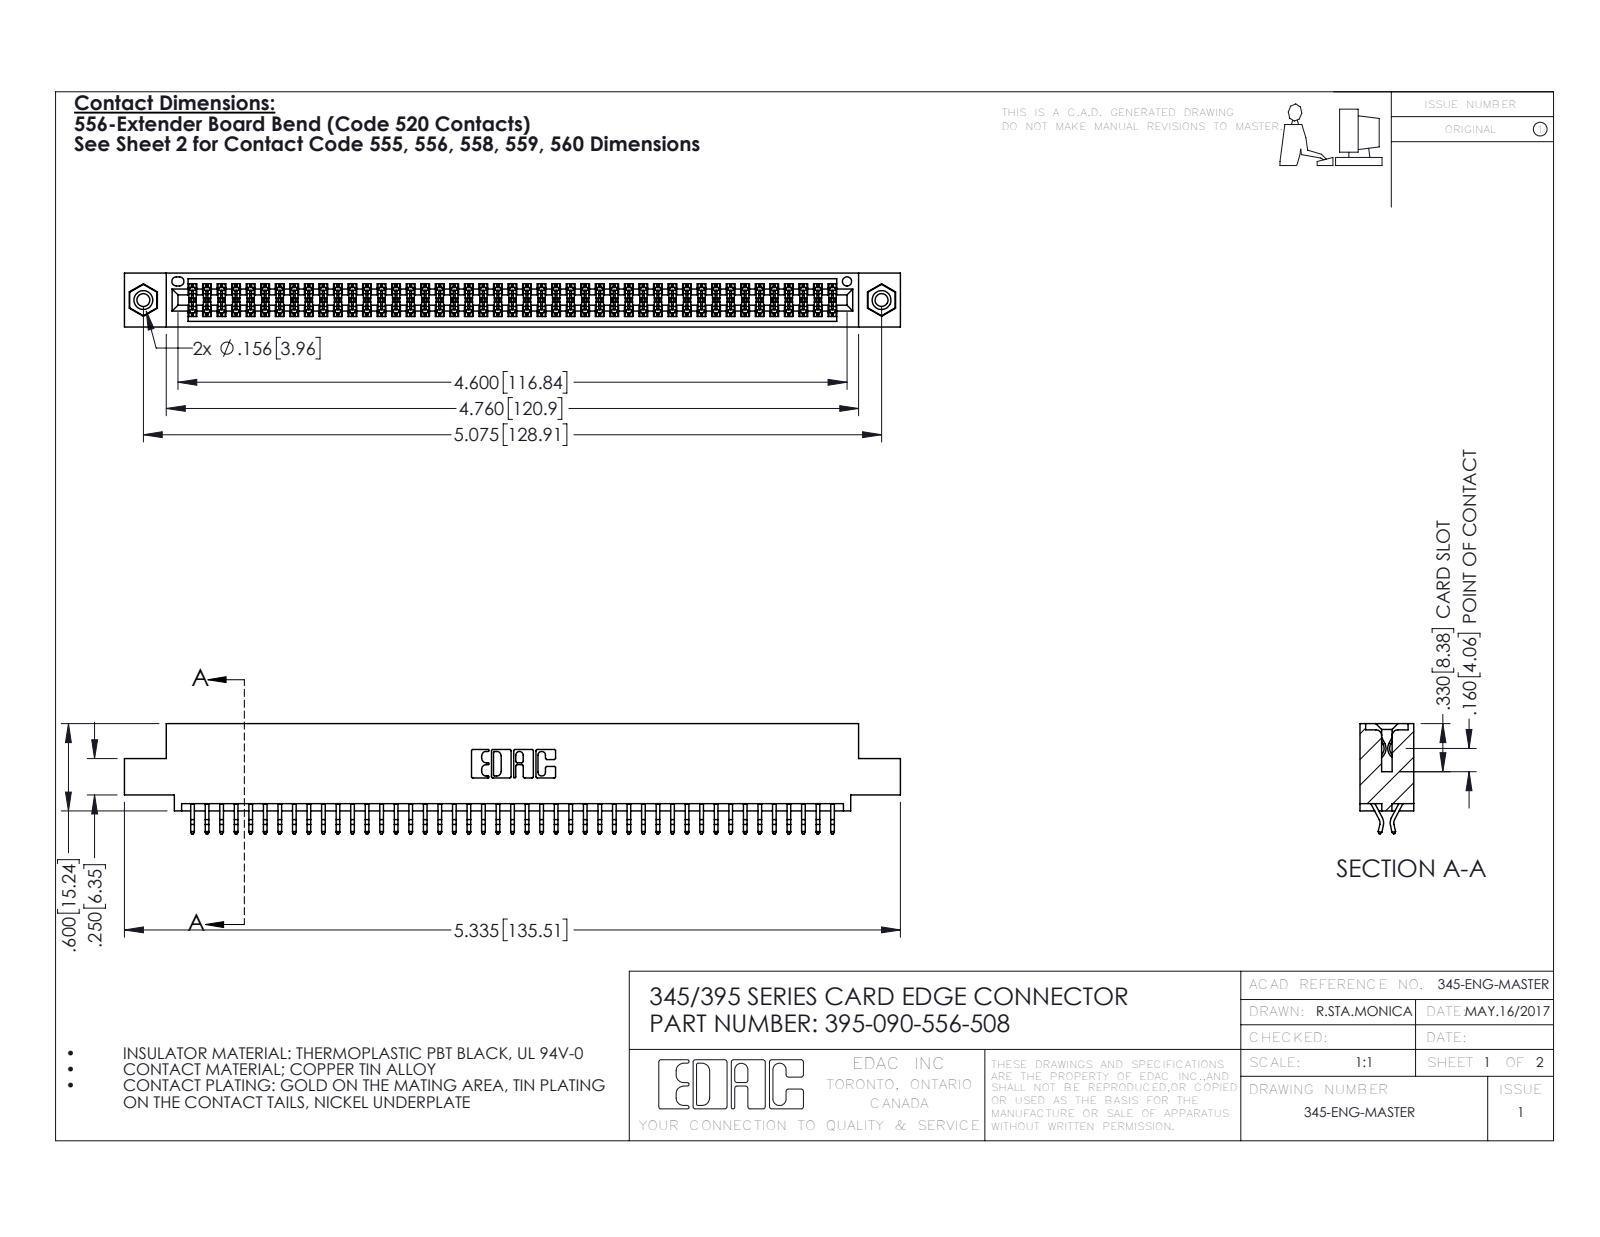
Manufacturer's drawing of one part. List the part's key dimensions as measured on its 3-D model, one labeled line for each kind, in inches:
Part name (STEP PRODUCT): 345 Part_0.110 Offset - 0.156 Dia-TI; 345-292-001_556 Tail; 345-250-001_345-250-003-102; 395-090-556-508
STEP written by: SolidWorks 2016 (CONFIG_CONTROL_DESIGN)
Units: inches
Bodies: 93 solids, 5230 faces (3446 planar, 1768 cylindrical, 16 other)
Overall size (bounding box): 5.335 × 0.757 × 0.37
Volume: 0.8 in³ · Surface area: 30.16 in²
Round holes (diameter × count): ⌀0.089 ×2, ⌀0.125 ×2, ⌀0.156 ×2, ⌀0.064 ×1
Round bosses / shafts (diameter × count): ⌀0.155 ×2
Partial cylindrical surfaces — rounded edges, fillets, slot ends (radius × count): R0.006 ×135, R0.01 ×22, R0.007 ×6, R0.031 ×6, R0.026 ×3, R0.01 ×2, R0.014 ×2, R0.019 ×2
Main face-to-face distances: 0.072, 0.298, 0.37, 0.2, 0.025, 0.098, 0.272, 0.225, 0.175, 0.149
Hole centre spacings: 0.27, 4.839, 5.075
